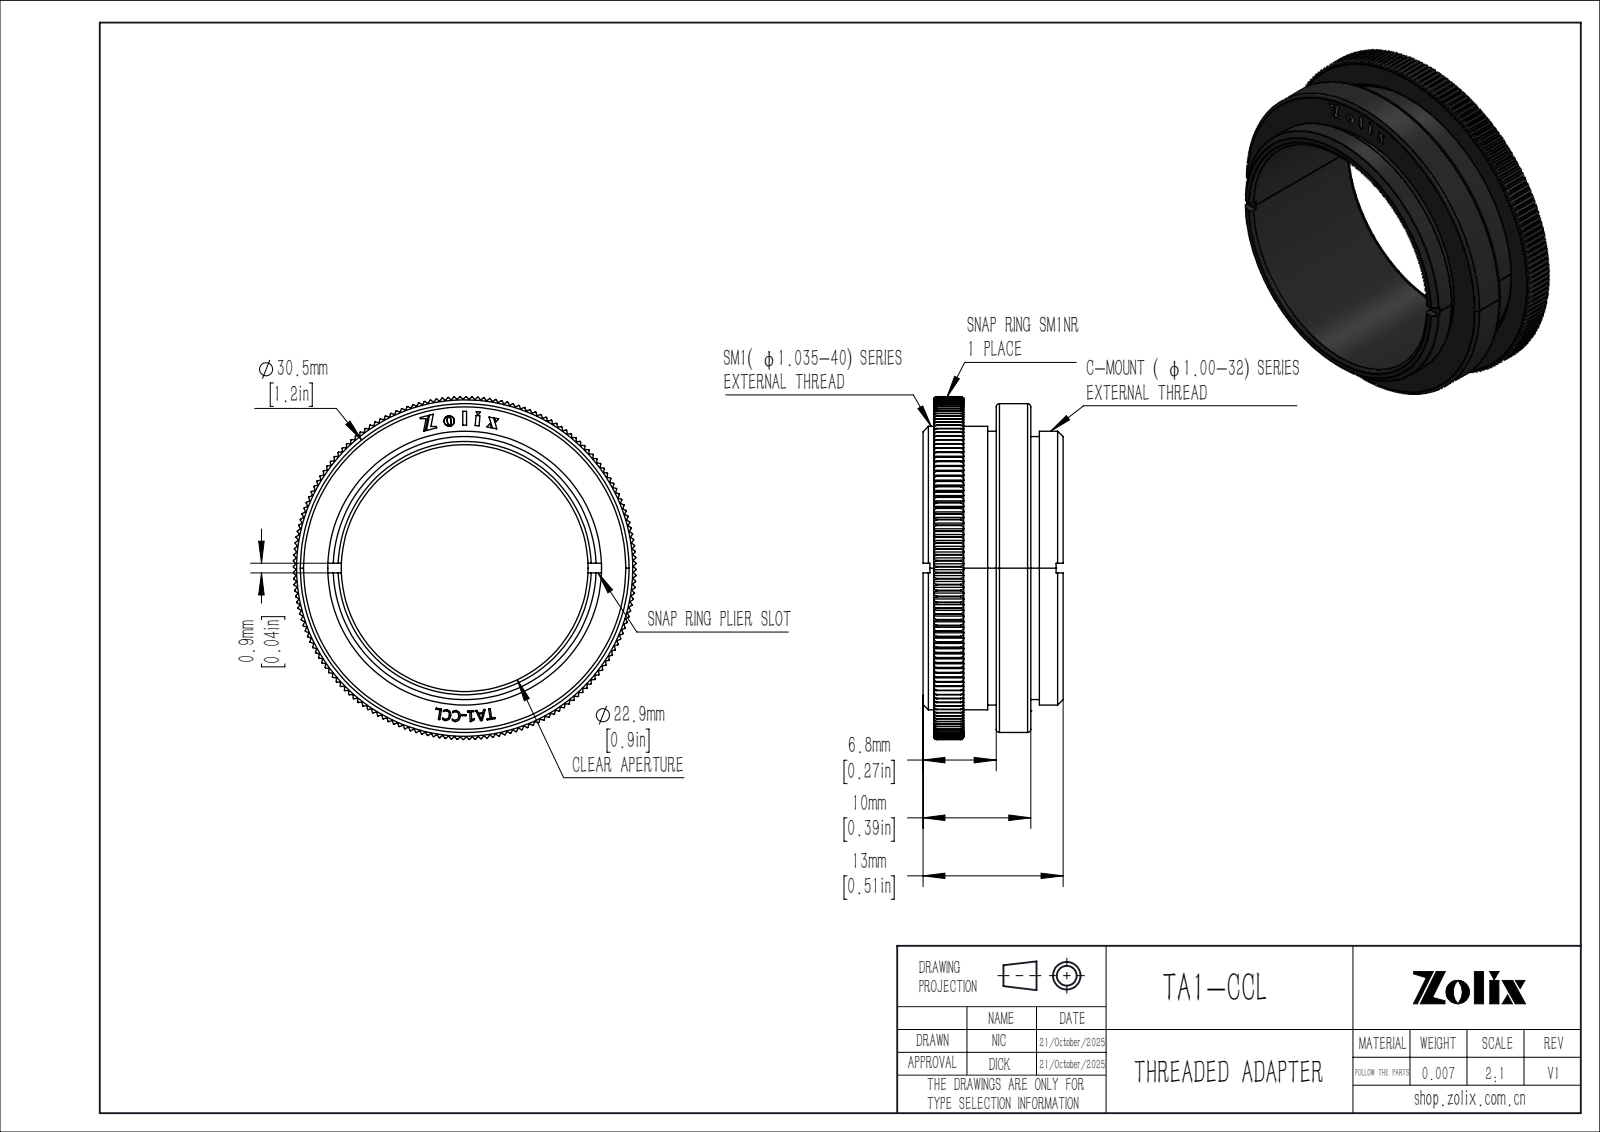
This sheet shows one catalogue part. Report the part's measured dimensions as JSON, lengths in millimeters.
{"part_name": "TA1-CCL", "step_written_by": "SolidWorks 2020 (CONFIG_CONTROL_DESIGN)", "units": "millimeters", "bodies": {"solids": 1, "faces": 1102, "planar": 773, "cylindrical": 194, "other": 135}, "overall_size": [31.8, 31.8, 13], "volume_mm3": 658, "surface_area_mm2": 3779, "round_holes": [[22.9, 1], [26.29, 1]], "round_bosses_or_shafts": [[30.5, 1], [25.4, 1], [24.4, 1]], "partial_cylinders_radius": [[15.9, 1]], "face_to_face_distances": [3.2, 3.01, 6.21, 2.8, 5.81, 9.01, 22.13, 0.8, 4, 0.99]}
